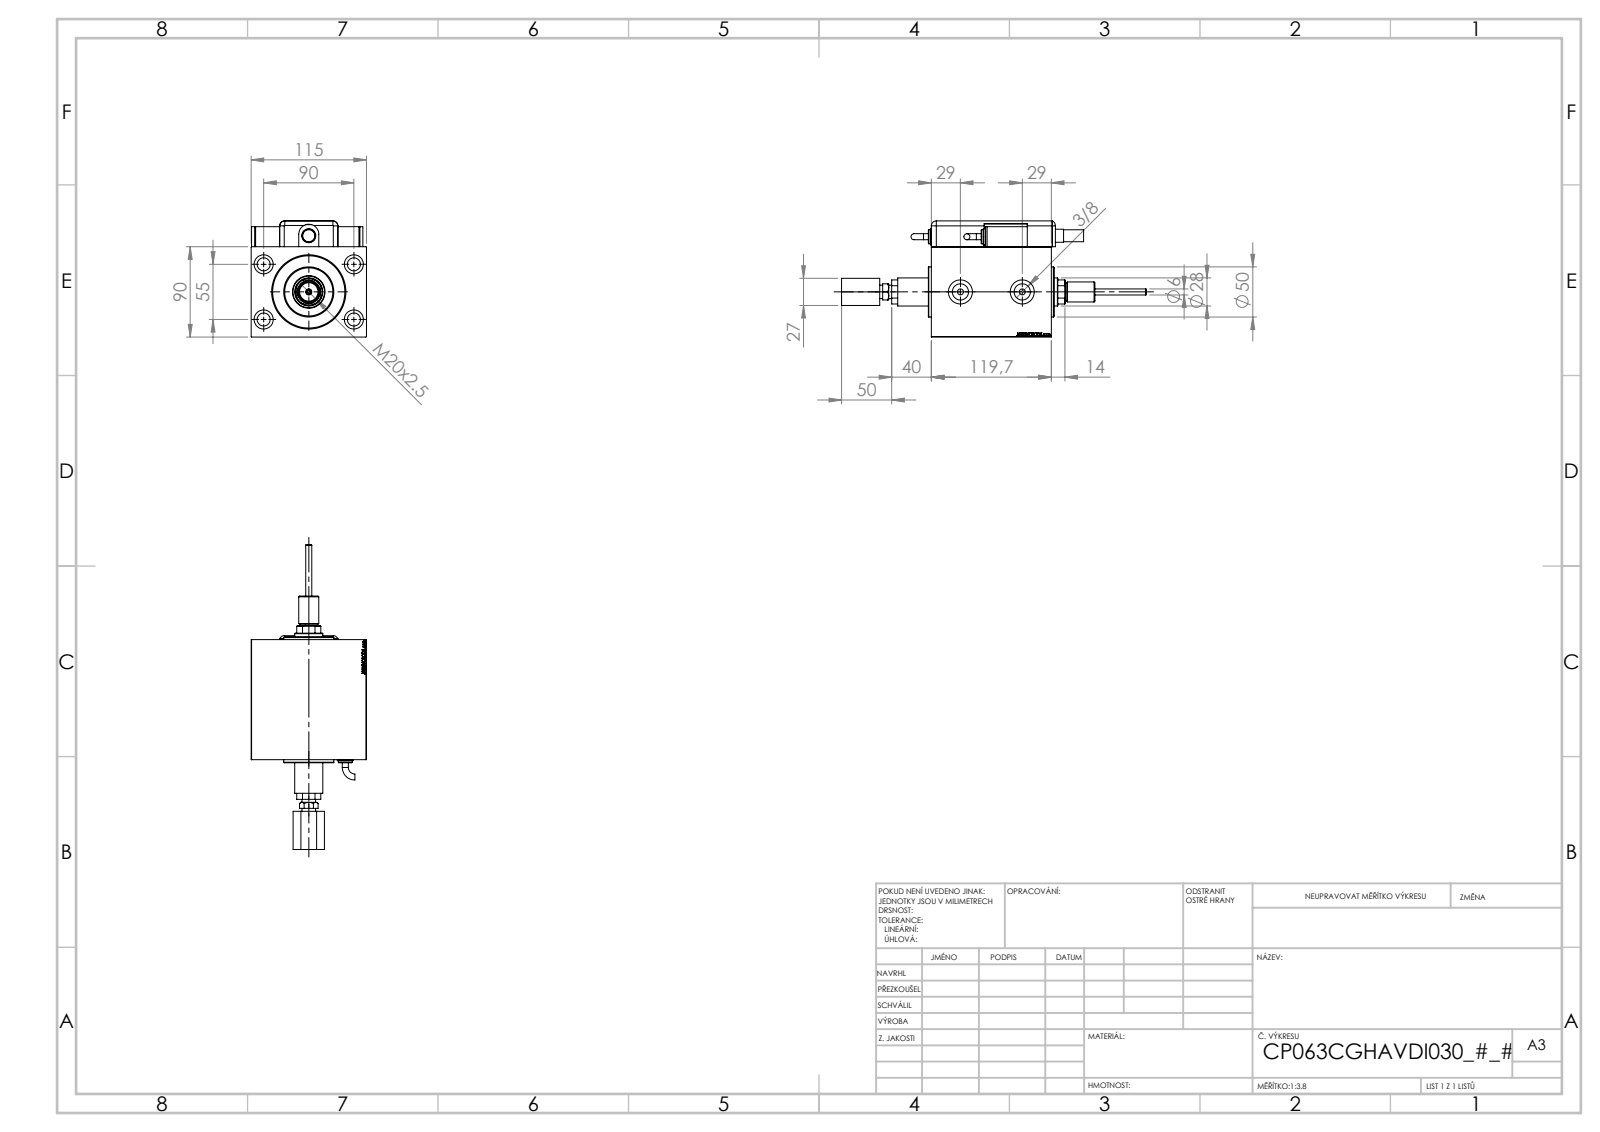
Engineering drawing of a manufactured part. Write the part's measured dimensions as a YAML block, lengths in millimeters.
part_name: "MAGNETIC SWITCH Q; V450DCP_C_Body; KRYT; V450DCP_VC_B (+6 more)"
step_written_by: "SolidWorks 2019 (CONFIG_CONTROL_DESIGN)"
units: millimeters
bodies: {solids: 11, faces: 1306, planar: 626, cylindrical: 149, other: 531}
overall_size: [303.7, 115.8, 115]
volume: 1279000
surface_area: 228089
round_holes:
  - {diameter: 4, count: 4}
  - {diameter: 13, count: 4}
  - {diameter: 19, count: 4}
  - {diameter: 6, count: 3}
  - {diameter: 8, count: 2}
  - {diameter: 9.73, count: 2}
  - {diameter: 15, count: 2}
  - {diameter: 16.17, count: 2}
  - {diameter: 24, count: 2}
  - {diameter: 3, count: 1}
  - {diameter: 14, count: 1}
  - {diameter: 18.5, count: 1}
round_bosses_or_shafts:
  - {diameter: 20, count: 3}
  - {diameter: 16, count: 2}
  - {diameter: 14, count: 2}
  - {diameter: 6, count: 2}
  - {diameter: 50, count: 1}
  - {diameter: 18, count: 1}
  - {diameter: 13.47, count: 1}
  - {diameter: 13, count: 1}
partial_cylinders:
  - {radius: 5, count: 9}
  - {radius: 10, count: 1}
  - {radius: 13.5, count: 1}
face_to_face_distances: [90, 3, 115, 119.7, 1, 17.5, 102.2, 30, 25.8, 115.8]
hole_center_spacings: [52.74, 53.27, 55, 90, 94.85, 105.48, 20, 22.18]
